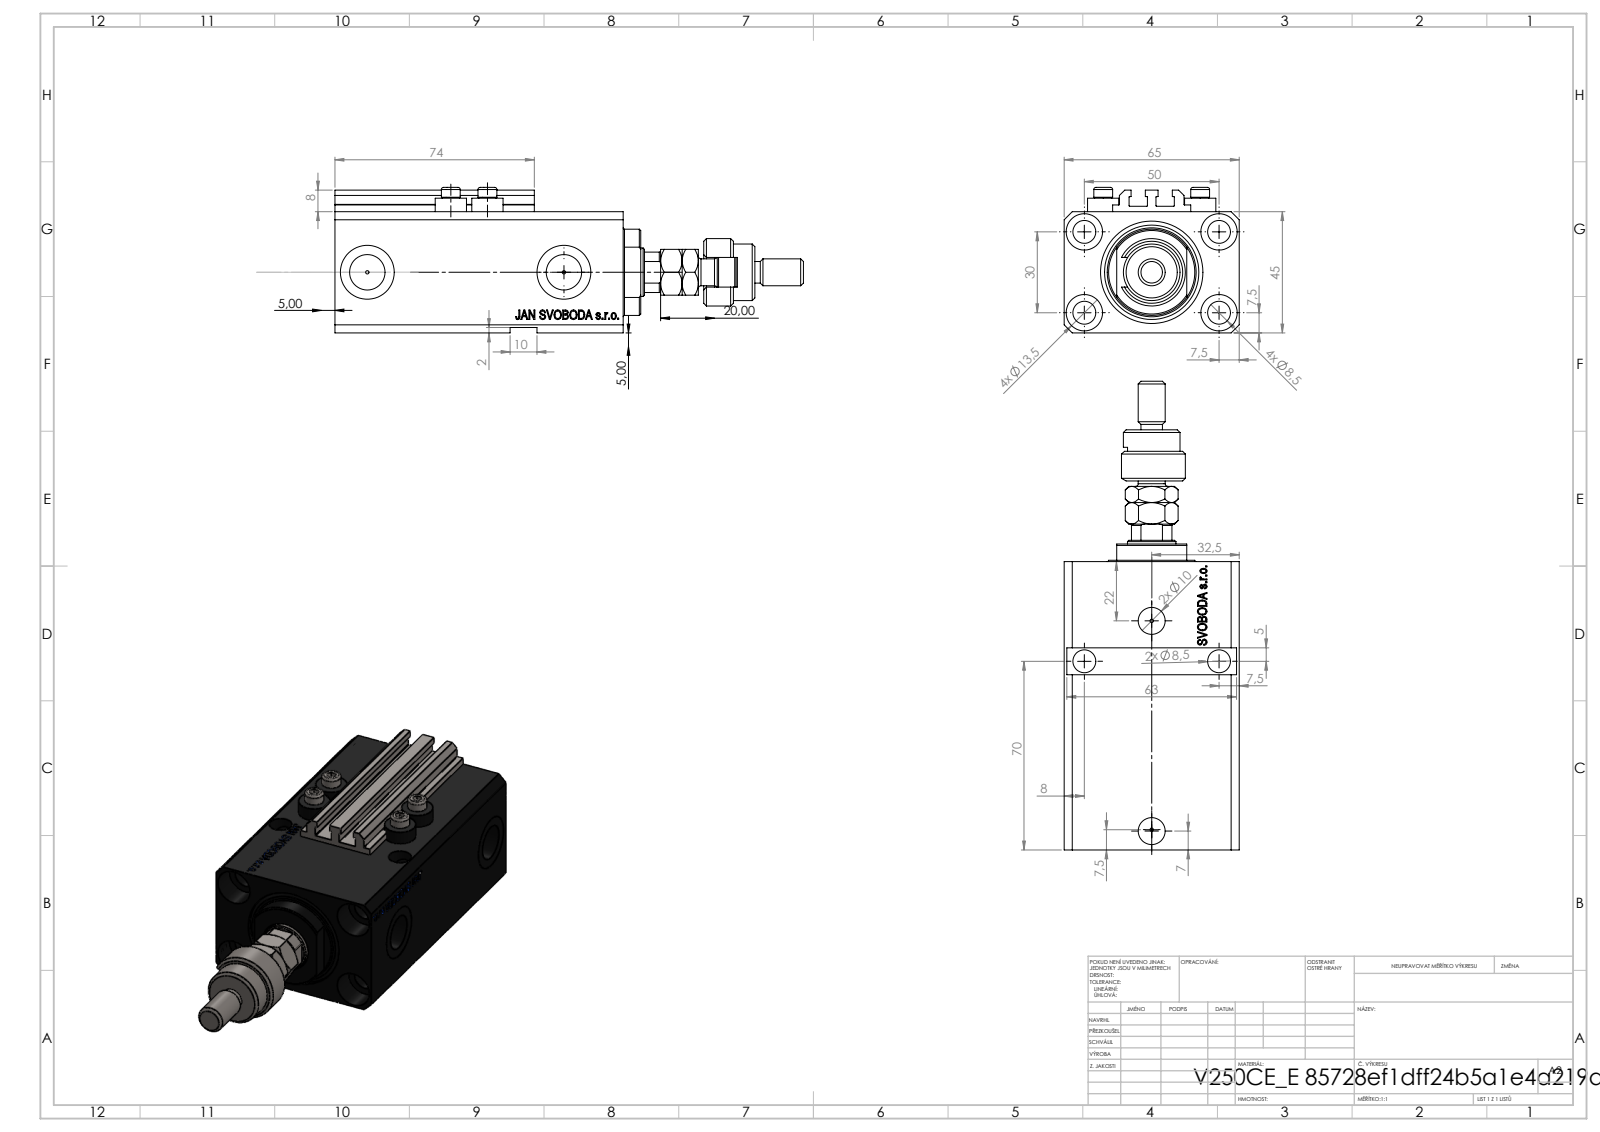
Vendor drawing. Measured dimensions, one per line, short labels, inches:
name: ALLEN BOLT V250CE; MFA; FEMALE_PART_FOR_DFA; V250CE_VC_E (+2 more)
written by: SolidWorks 2019 (CONFIG_CONTROL_DESIGN)
unit: in
bodies: 10 solids, 1188 faces (543 planar, 171 cylindrical, 474 other)
size: 6.85 × 2.559 × 2.126
volume: 17.18 in³; area: 129.4 in²
holes: 9× ⌀0.335, 4× ⌀0.049, 4× ⌀0.157, 4× ⌀0.531, 2× ⌀0.394, 2× ⌀0.518, 2× ⌀0.787, 1× ⌀0.709, 1× ⌀1.496
bosses: 4× ⌀0.457, 4× ⌀0.276, 1× ⌀0.984, 1× ⌀0.827, 1× ⌀0.63, 1× ⌀0.394, 1× ⌀0.315
rounds: 10× R0.008, 1× R0.217, 1× R0.335, 1× R0.344, 1× R0.63
face distances: 1.772, 2.559, 0.551, 0.079, 3.661, 1.85, 4.213, 0.098, 0.118, 0.394
hole spacings: 1.148, 1.969, 0.535, 0.581, 0.595, 1.083, 1.098, 1.181
